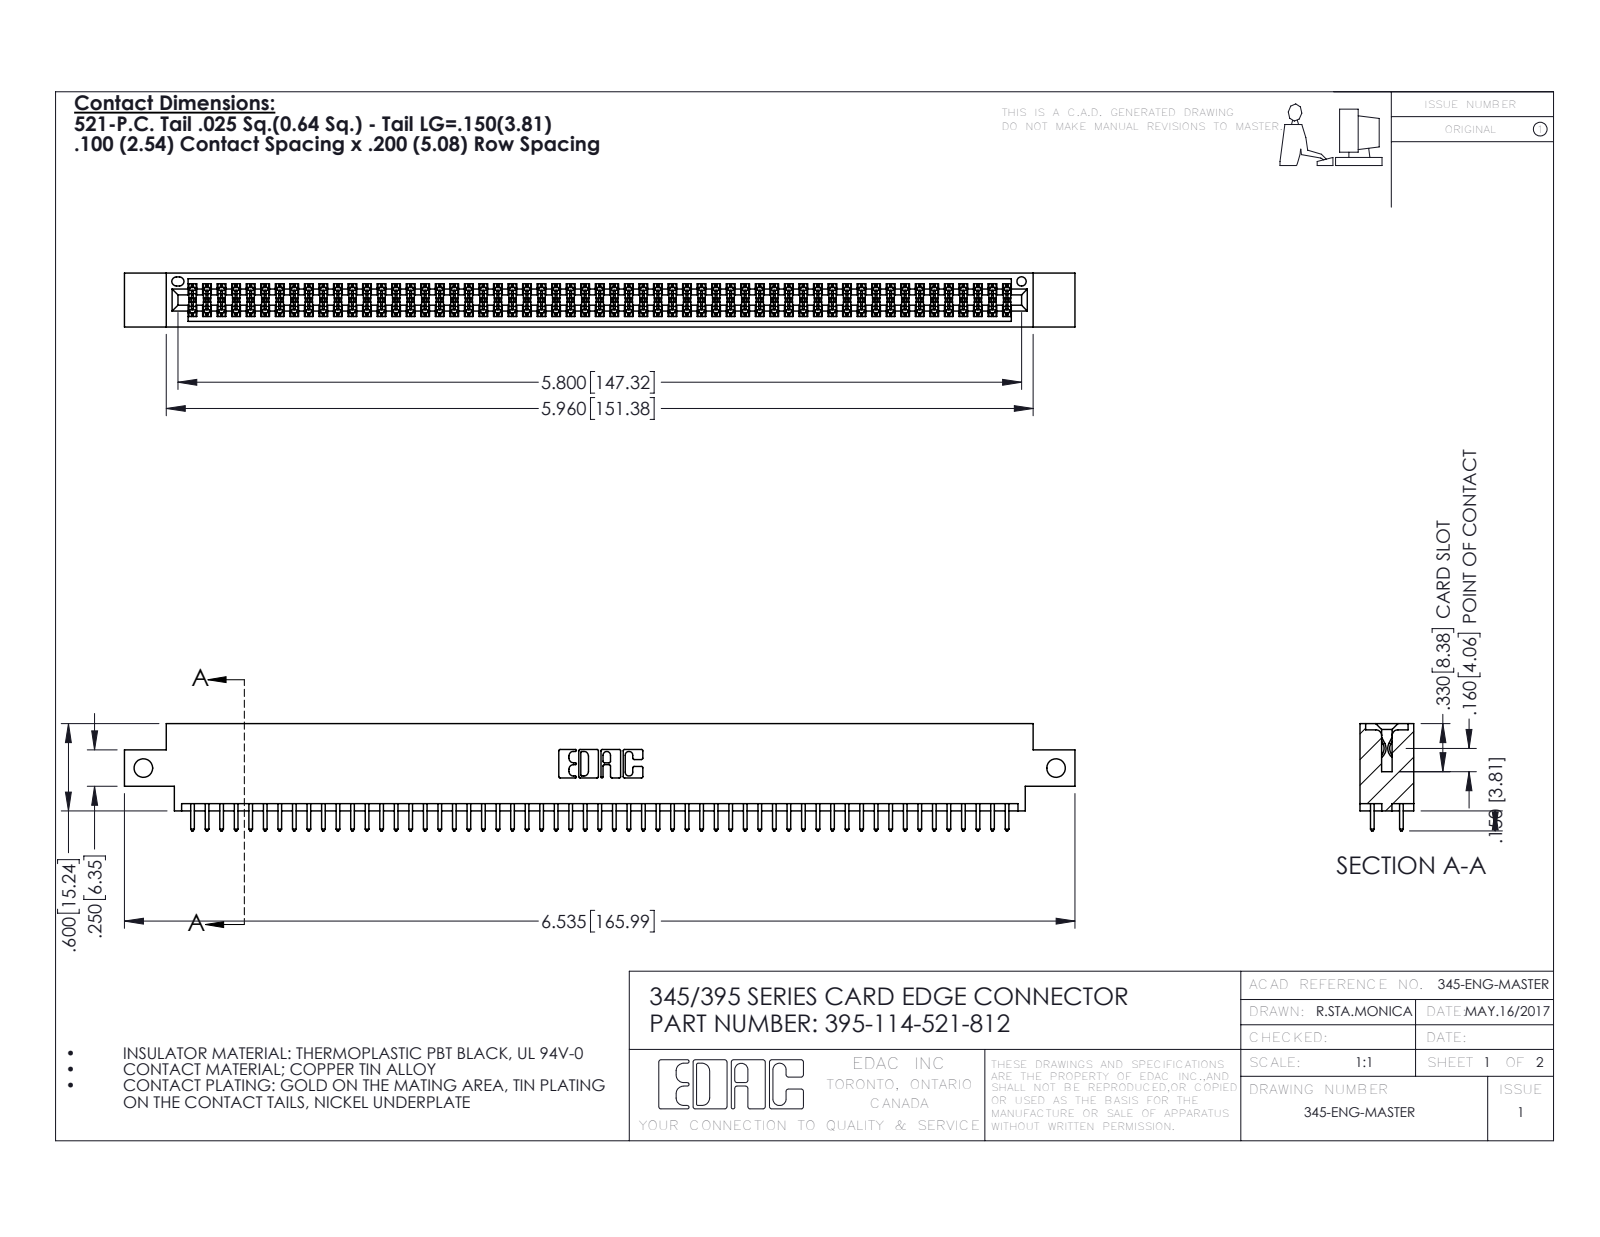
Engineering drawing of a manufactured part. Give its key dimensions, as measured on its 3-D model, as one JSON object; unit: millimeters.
{"part_name": "345 Part_0.170 Offset - Side Mount; 395-114-521-812; 345-292-001_345-293-121", "step_written_by": "SolidWorks 2016 (CONFIG_CONTROL_DESIGN)", "units": "millimeters", "bodies": {"solids": 115, "faces": 5830, "planar": 3846, "cylindrical": 1984, "other": 0}, "overall_size": [166, 18.7, 9.4], "volume_mm3": 16000, "surface_area_mm2": 23670, "round_holes": [[3.3, 2], [1.6, 1]], "partial_cylinders_radius": [[0.2, 171], [0.3, 114], [0.3, 22], [0.2, 6], [0.8, 6], [0.7, 3], [0.4, 2], [0.5, 2]], "face_to_face_distances": [1.8, 7.6, 9.4, 5.1, 2.5, 6.9, 0.6, 5.7, 4.4, 3.8], "hole_center_spacings": [159.4]}
